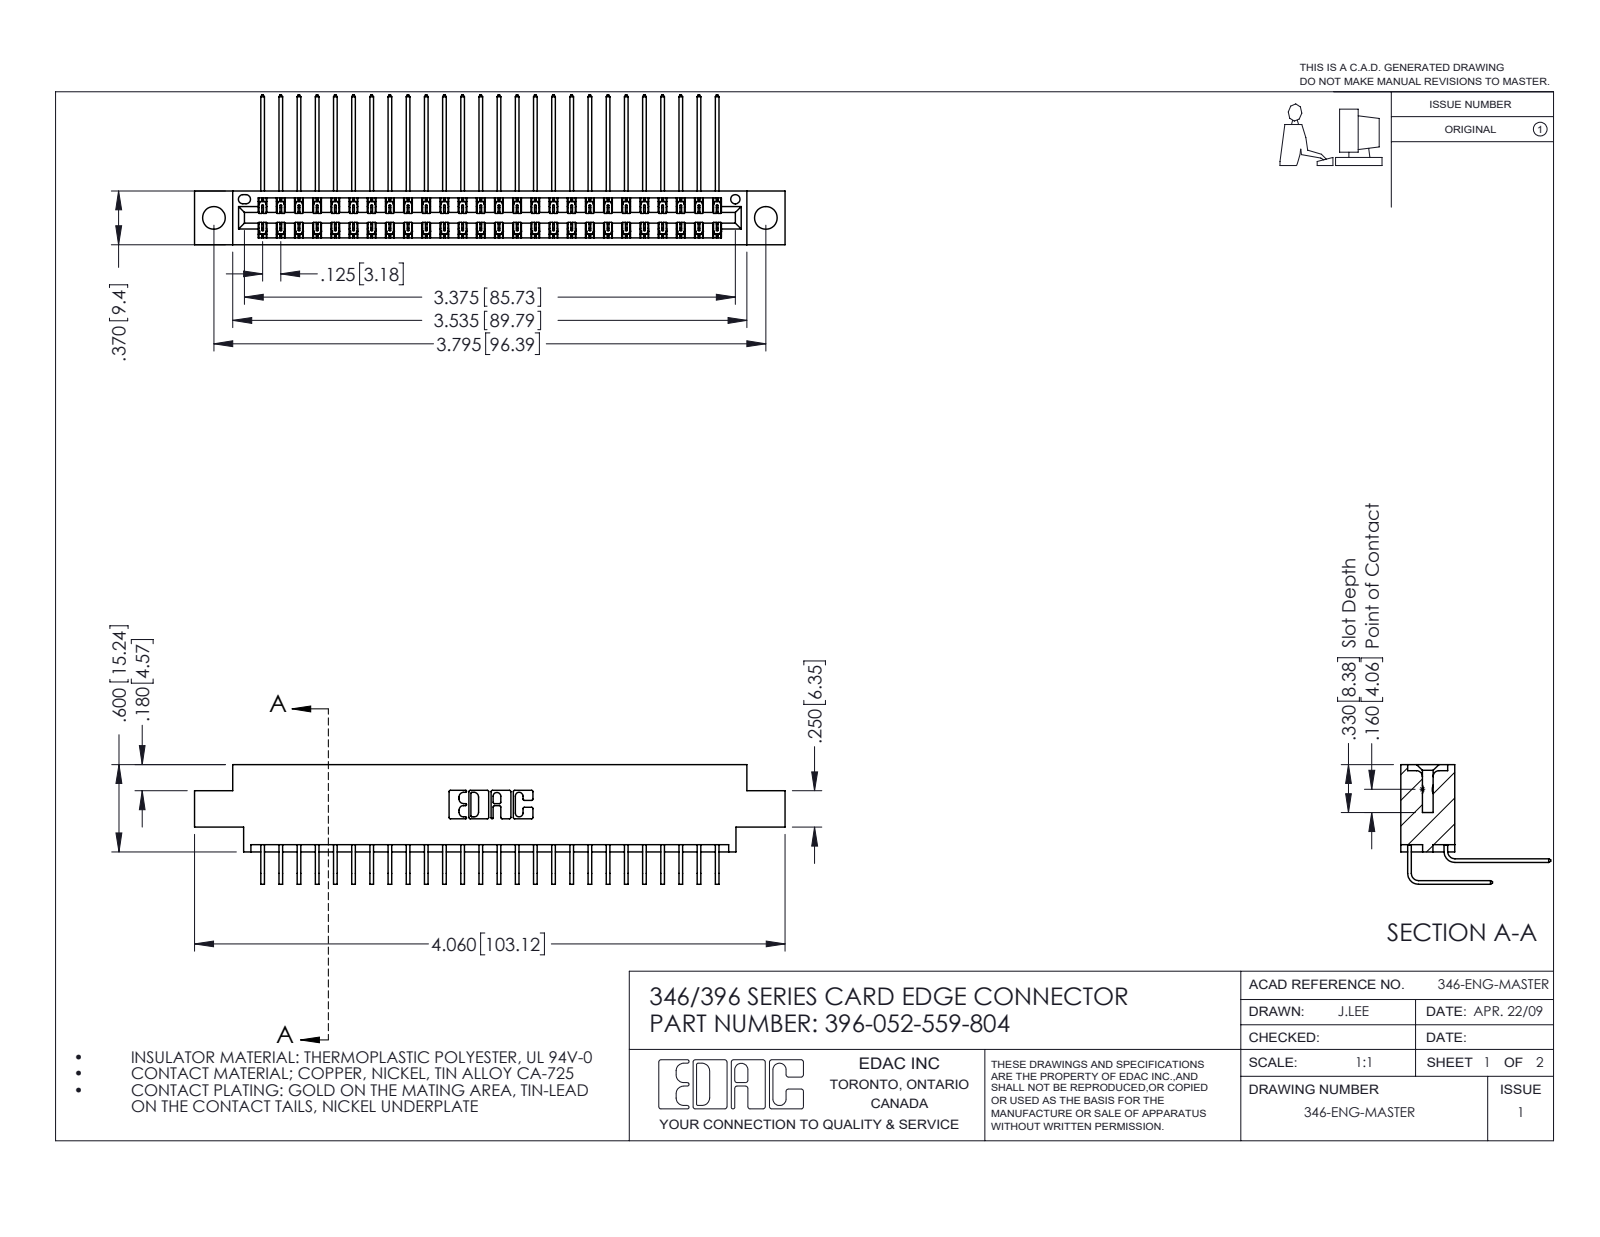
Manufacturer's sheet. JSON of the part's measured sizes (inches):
{"part_name": "346 Part_0.170 Offset - 0.156 Dia-TH; 396-052-559-804; 345-292-001_559 Tail - 2; 345-292-001_558 559 Tail - 1", "step_written_by": "SolidWorks 2016 (CONFIG_CONTROL_DESIGN)", "units": "inches", "bodies": {"solids": 53, "faces": 2934, "planar": 2004, "cylindrical": 930, "other": 0}, "overall_size": [4.06, 1.03, 0.823], "volume_in3": 0.61, "surface_area_in2": 23.11, "round_holes": [[0.156, 2], [0.064, 1]], "partial_cylinders_radius": [[0.006, 78], [0.01, 22], [0.007, 6], [0.031, 6], [0.026, 3], [0.014, 2], [0.022, 2], [0.024, 2]], "face_to_face_distances": [0.048, 0.322, 0.025, 0.37, 0.25, 0.072, 0.298, 0.275, 0.148, 0.222], "hole_center_spacings": [0.246, 3.587, 3.795]}
